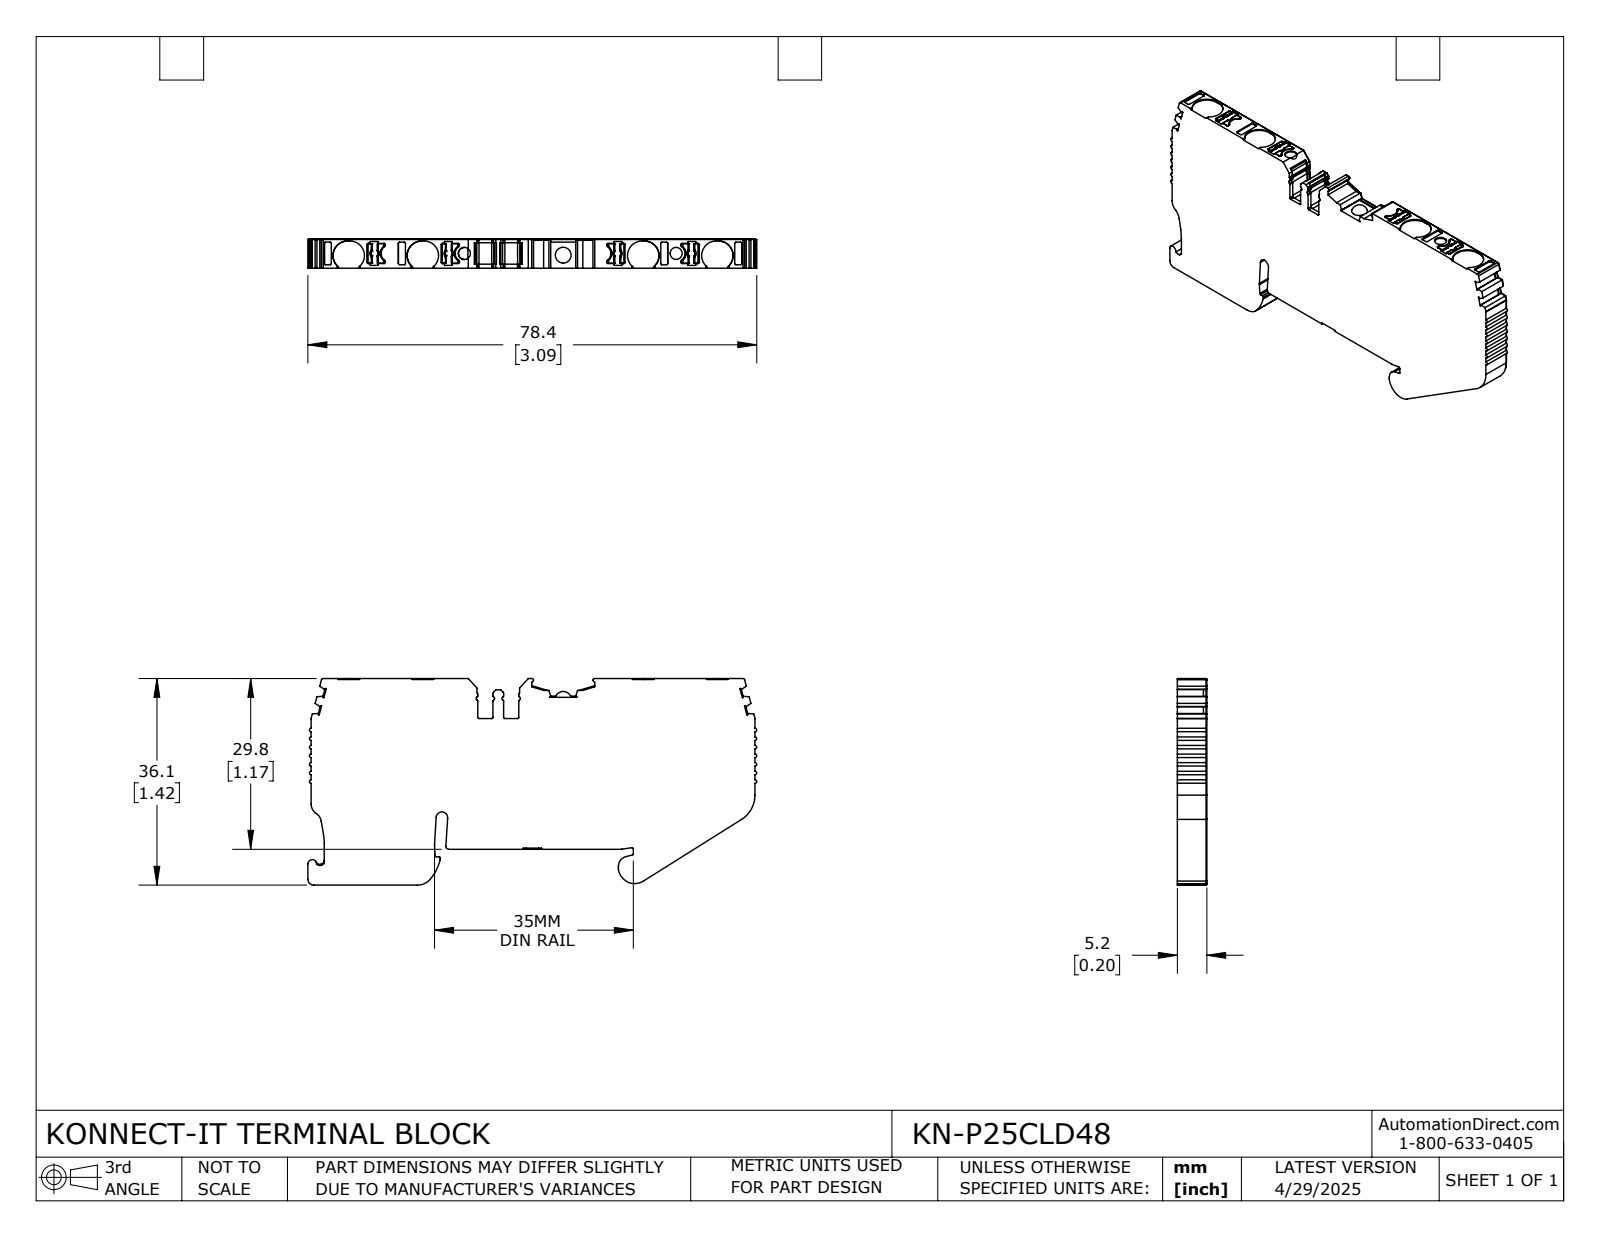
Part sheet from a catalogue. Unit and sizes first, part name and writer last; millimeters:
Units: millimetres
Overall size (bounding box): 78.36 × 36.07 × 5.15
Round holes (diameter × count): ⌀2.1 ×2
Partial cylindrical surfaces — rounded edges, fillets, slot ends (radius × count): R0.2 ×78, R0.3 ×39, R0.1 ×21, R0.5 ×18, R0.15 ×16, R0.4 ×9, R2.55 ×8, R1.5 ×4
Main face-to-face distances: 5.15, 29.61, 29.81, 6.26, 35.87, 36.07, 77.52, 1.2, 5, 4.5
Hole centre spacings: 36.98
Volume: 11 975 mm³ · Surface area: 6 221 mm²
Bodies: 1 solid, 740 faces (381 planar, 291 cylindrical, 68 other)
Part name (STEP PRODUCT): KN-P25CLD48
STEP written by: SolidWorks 2024 (CONFIG_CONTROL_DESIGN)
